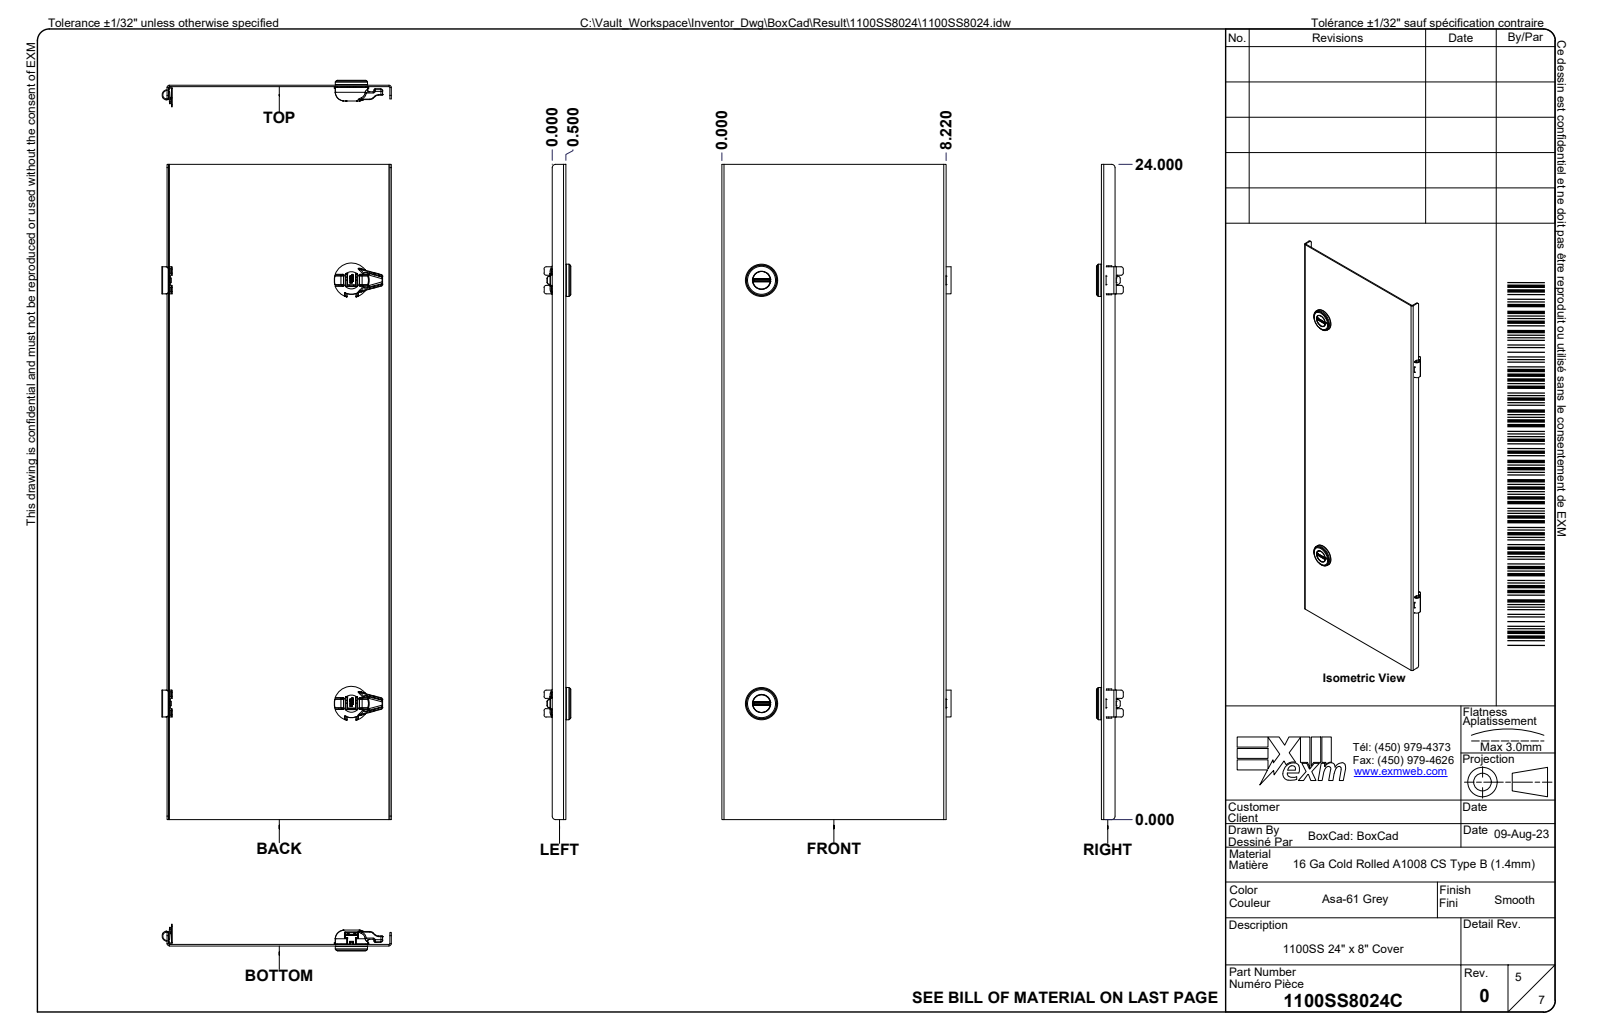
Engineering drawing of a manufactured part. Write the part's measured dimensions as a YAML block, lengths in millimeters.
part_name: "1100SS8024; 1100SS8024B; 1100SS8024B-P; 1100SS8024C (+7 more)"
step_written_by: "Autodesk Inventor 2024 (AUTOMOTIVE_DESIGN)"
units: millimeters
bodies: {solids: 8, faces: 3376, planar: 1278, cylindrical: 902, other: 1196}
overall_size: [609.6, 213.5, 209.2]
volume: 745400
surface_area: 1069000
round_holes:
  - {diameter: 7.1, count: 12}
  - {diameter: 0.8, count: 2}
  - {diameter: 22.2, count: 2}
  - {diameter: 28.6, count: 2}
round_bosses_or_shafts:
  - {diameter: 32, count: 2}
  - {diameter: 30, count: 2}
  - {diameter: 28.6, count: 2}
  - {diameter: 22.2, count: 2}
  - {diameter: 20, count: 2}
partial_cylinders:
  - {radius: 0.3, count: 388}
  - {radius: 0.5, count: 37}
  - {radius: 2, count: 20}
  - {radius: 0.2, count: 13}
  - {radius: 1, count: 7}
  - {radius: 0.6, count: 6}
  - {radius: 0.8, count: 6}
  - {radius: 2.2, count: 6}
face_to_face_distances: [1.4, 201.8, 203.2, 200.4, 204.6, 2.8, 2.8, 4.2, 204.6, 206]
hole_center_spacings: [152.4, 50.8, 160.6, 533.4, 554.7, 584.2, 603.8, 140.3]
